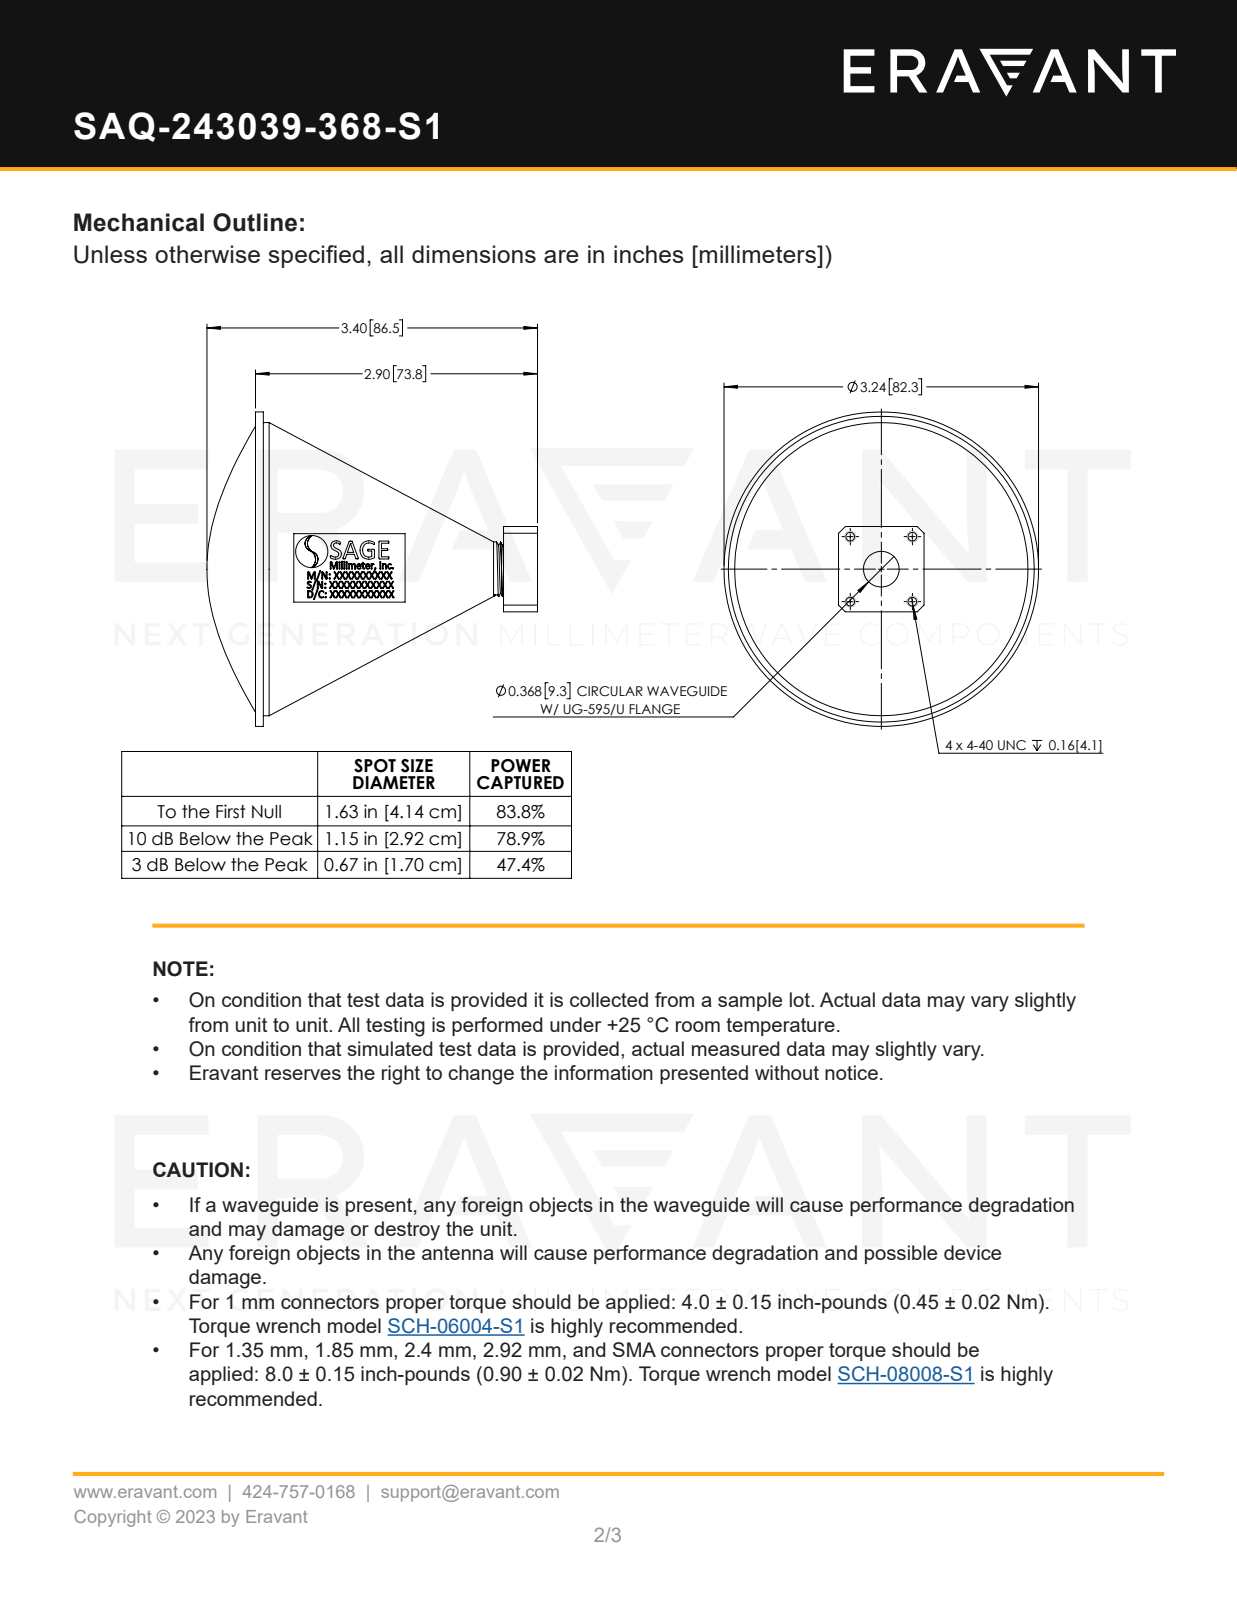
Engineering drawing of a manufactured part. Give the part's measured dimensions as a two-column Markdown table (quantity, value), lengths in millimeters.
| quantity | value |
| --- | --- |
| part name | SAQ-243039-368-S1 |
| STEP written by | SolidWorks 2016 (CONFIG_CONTROL_DESIGN) |
| units | millimeters |
| bodies | 3 solids, 78 faces (24 planar, 48 cylindrical, 6 other) |
| overall size | 86.5 × 82.3 × 82.3 |
| volume | 159 100 mm³ |
| surface area | 30 490 mm² |
| round holes (diameter × count) | 2.3 × 4, 4.8 × 4, 9.3 × 1, 13.1 × 1, 74.9 × 1, 80 × 1 |
| round bosses / shafts (diameter × count) | 82.3 × 1, 76.7 × 1, 14.3 × 1, 12.2 × 1 |
| main face-to-face distances | 2.5, 71.2, 73.8, 72.5, 1.2, 1.3, 22.4, 71.7, 0.5, 0.8 |
| hole center spacings | 11.8, 16.3, 17, 23.5 |
